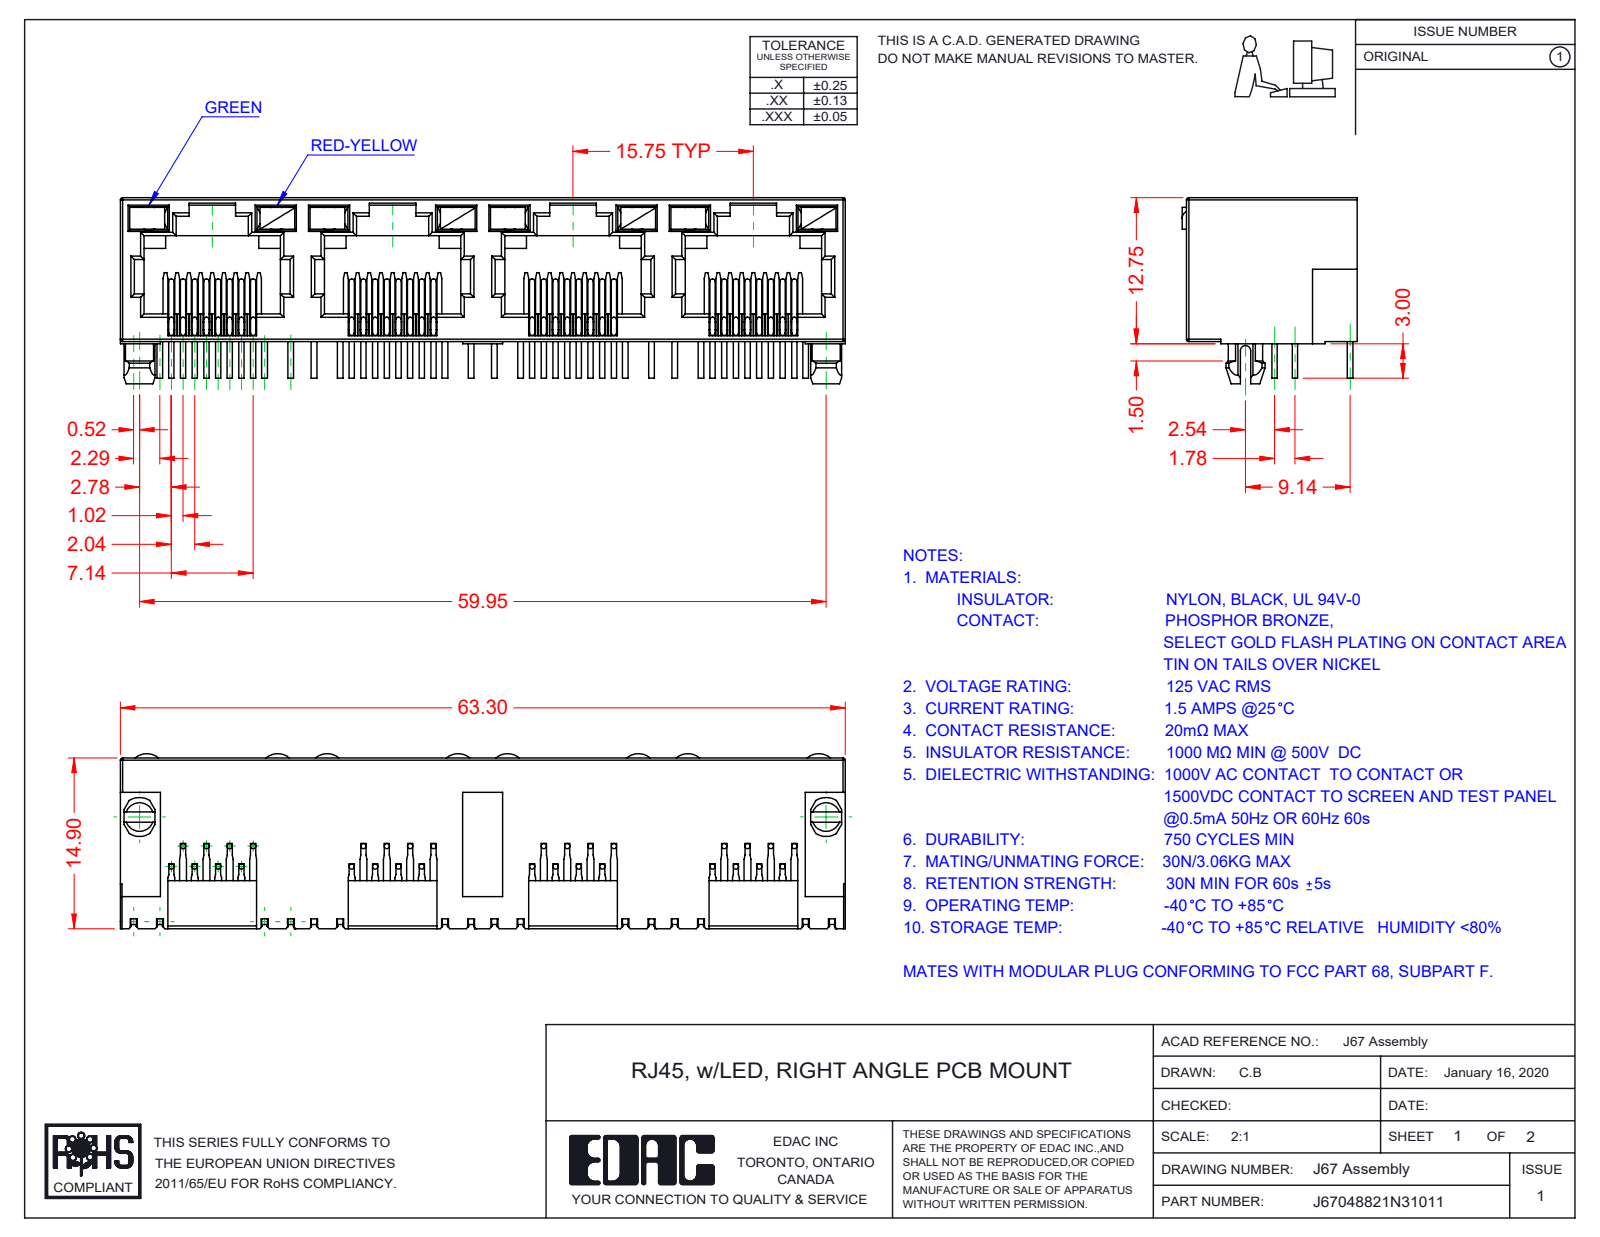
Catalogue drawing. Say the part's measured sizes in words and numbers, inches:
The part is named "67 LED LH_3-Green; 67 LED RH_8-Red-Yellow; J67048822N38011; 67 Contacts (+1 more)". Its 3-D file was written by "SolidWorks 2016 (CONFIG_CONTROL_DESIGN)". It is 41 solids with 2473 faces: 1781 planar, 484 cylindrical and 208 other. Overall it measures 2.492 by 0.64 by 0.602 inches. Its volume is 0.315 cubic inches and its surface area 17.94 square inches. Round bosses or shafts: 96 of diameter 0.018. Partial cylindrical surfaces (rounded edges, fillets, slot ends): 66 of radius 0.008, 29 of radius 0.012, 9 of radius 0.018, 8 of radius 0.061, 2 of radius 0.059, 2 of radius 0.067, 1 of radius 0.014, 1 of radius 0.039. The main face-to-face distances are 0.02, 0.494, 0.074, 0.035, 0.394, 0.62, 0.039, 0.055, 0.433, 0.468.
